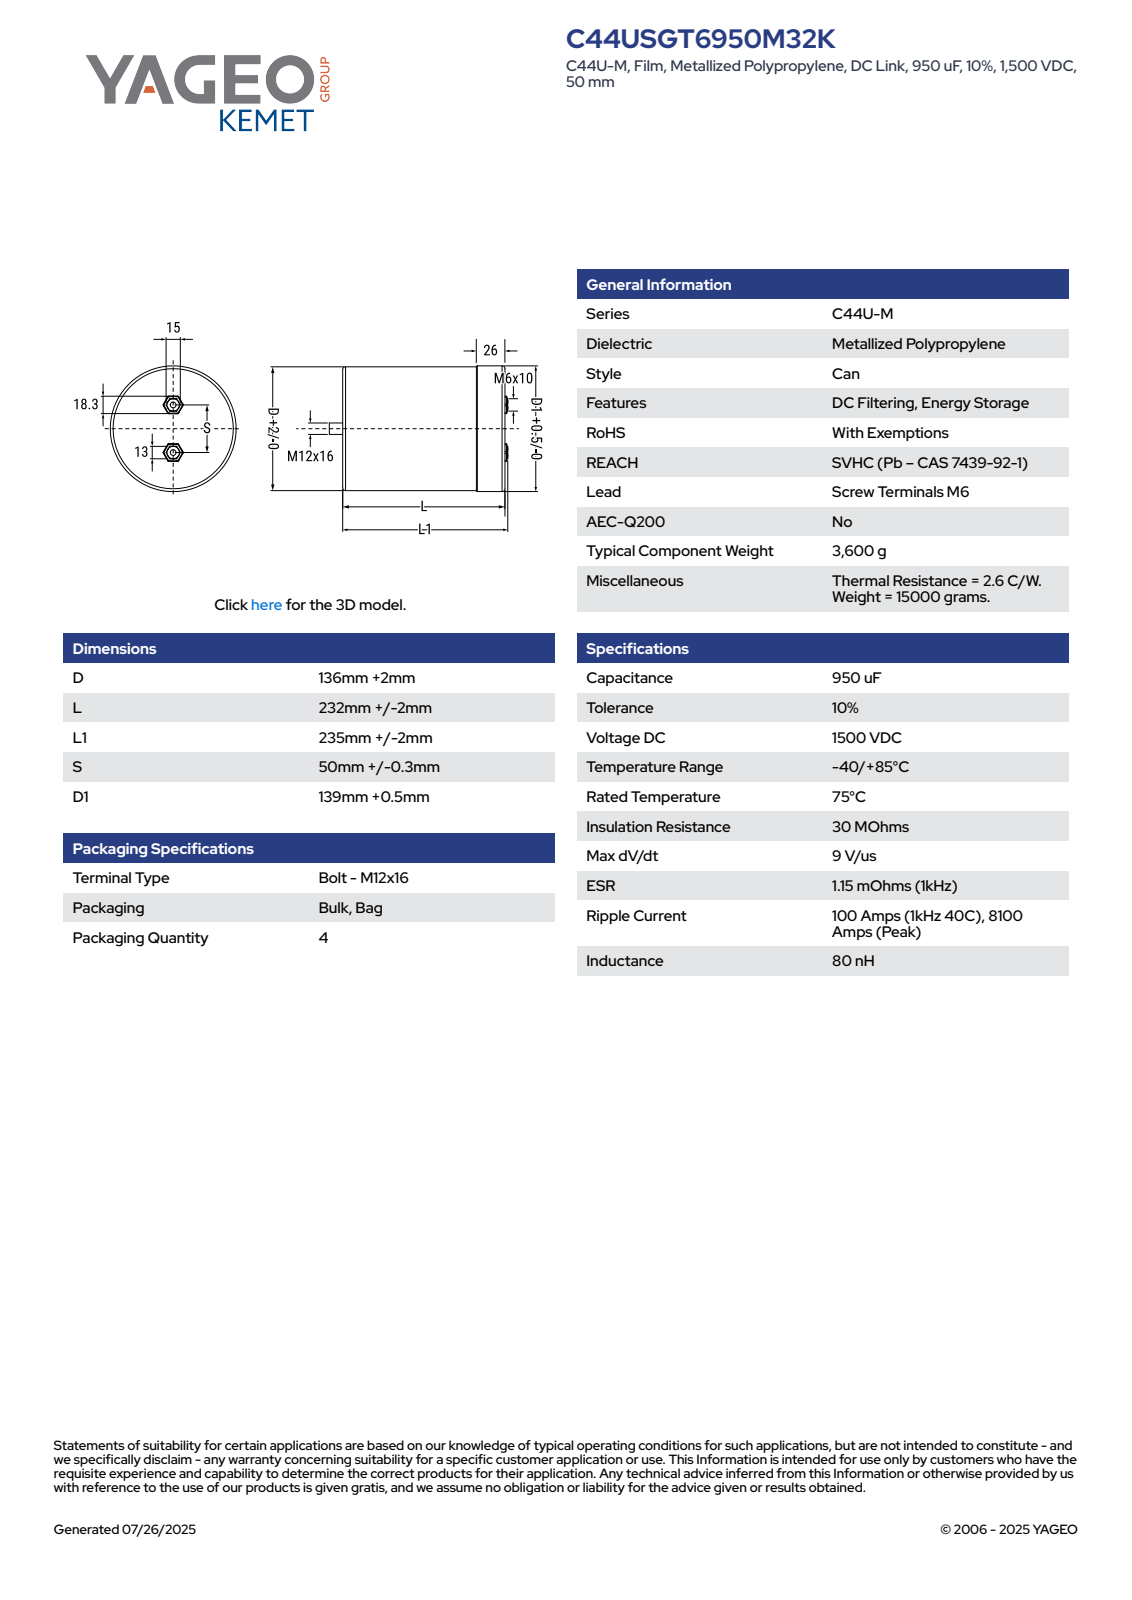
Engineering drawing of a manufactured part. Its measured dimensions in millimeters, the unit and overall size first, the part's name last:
Units: millimetres
Overall size (bounding box): 253 × 139.5 × 139.5
Round holes (diameter × count): ⌀6 ×2
Round bosses / shafts (diameter × count): ⌀13 ×2, ⌀139.5 ×1, ⌀138 ×1, ⌀12 ×1
Partial cylindrical surfaces — rounded edges, fillets, slot ends (radius × count): R69.01 ×1
Main face-to-face distances: 234, 208, 26, 236, 28, 2, 237, 29, 3, 1
Hole centre spacings: 50
Volume: 3 511 000 mm³ · Surface area: 133 460 mm²
Bodies: 1 solid, 92 faces (44 planar, 17 cylindrical, 31 other)
Part name (STEP PRODUCT): CFP_C44UMH_136X232_D138L234S50L1237D1139.5
STEP written by: SolidWorks 2014 (AUTOMOTIVE_DESIGN)
